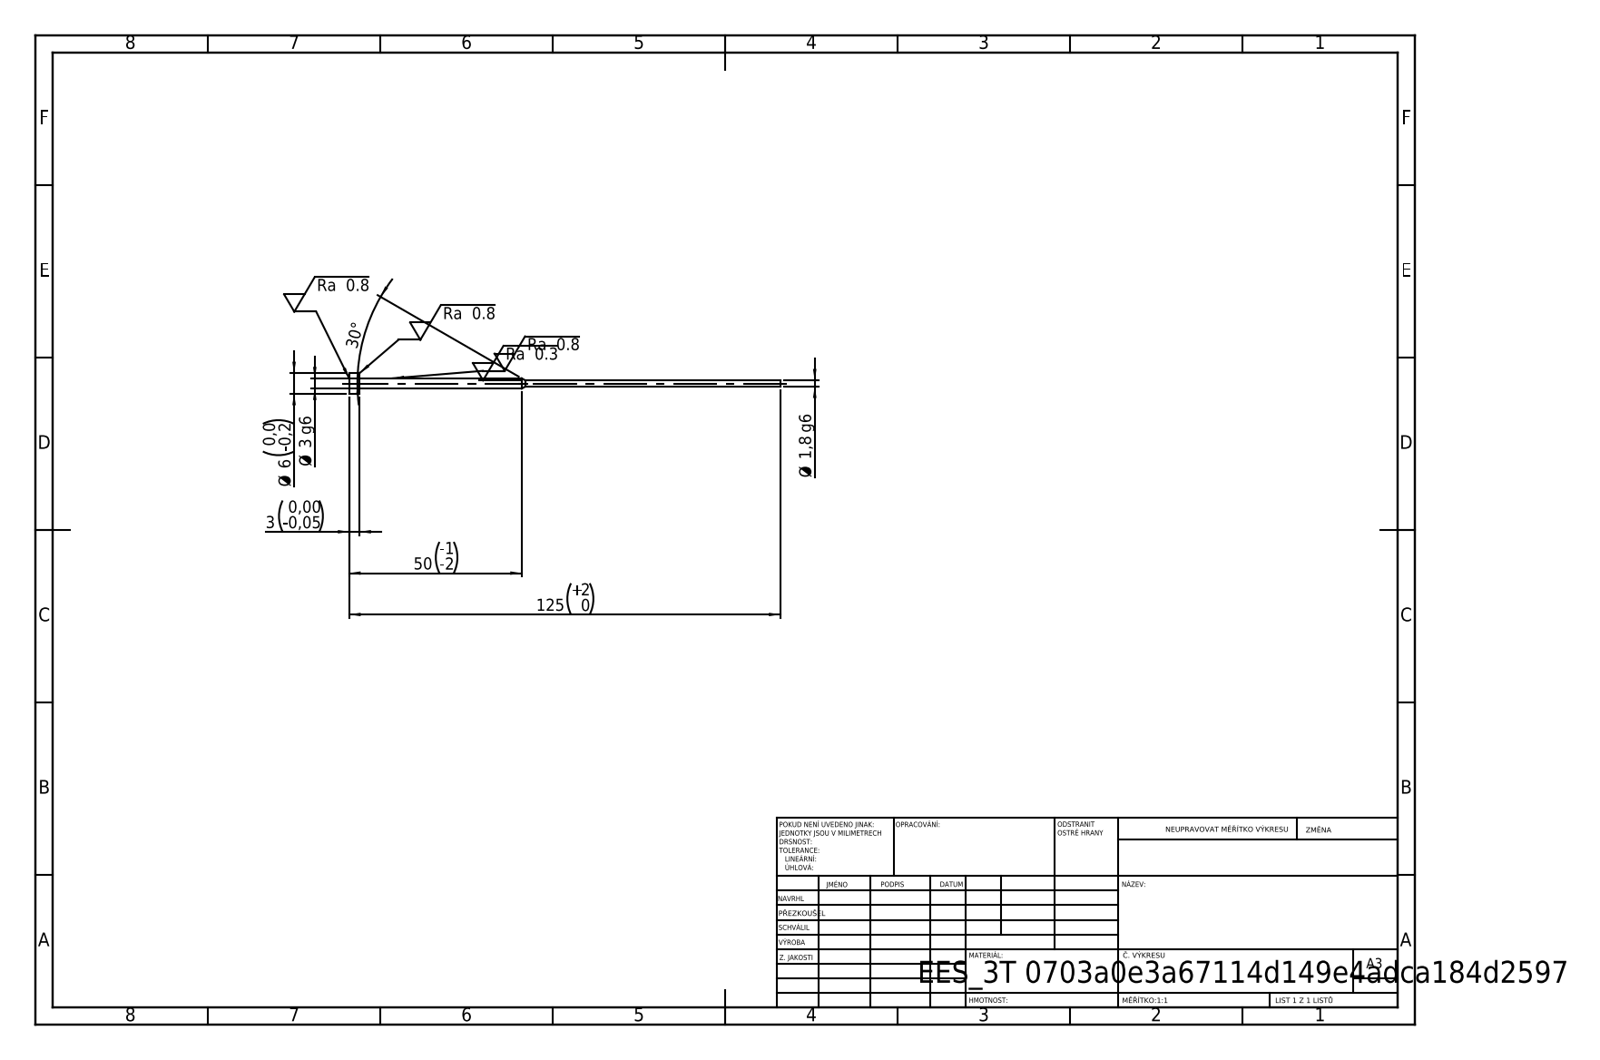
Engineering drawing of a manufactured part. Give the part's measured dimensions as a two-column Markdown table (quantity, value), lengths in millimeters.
| quantity | value |
| --- | --- |
| STEP written by | SolidWorks 2019 (CONFIG_CONTROL_DESIGN) |
| units | millimeters |
| bodies | 1 solid, 11 faces (3 planar, 6 cylindrical, 2 other) |
| overall size | 125 × 6 × 6 |
| volume | 610 mm³ |
| surface area | 979 mm² |
| round bosses / shafts (diameter × count) | 6 × 1, 3 × 1, 1.8 × 1 |
| main face-to-face distances | 3, 122, 125 |
